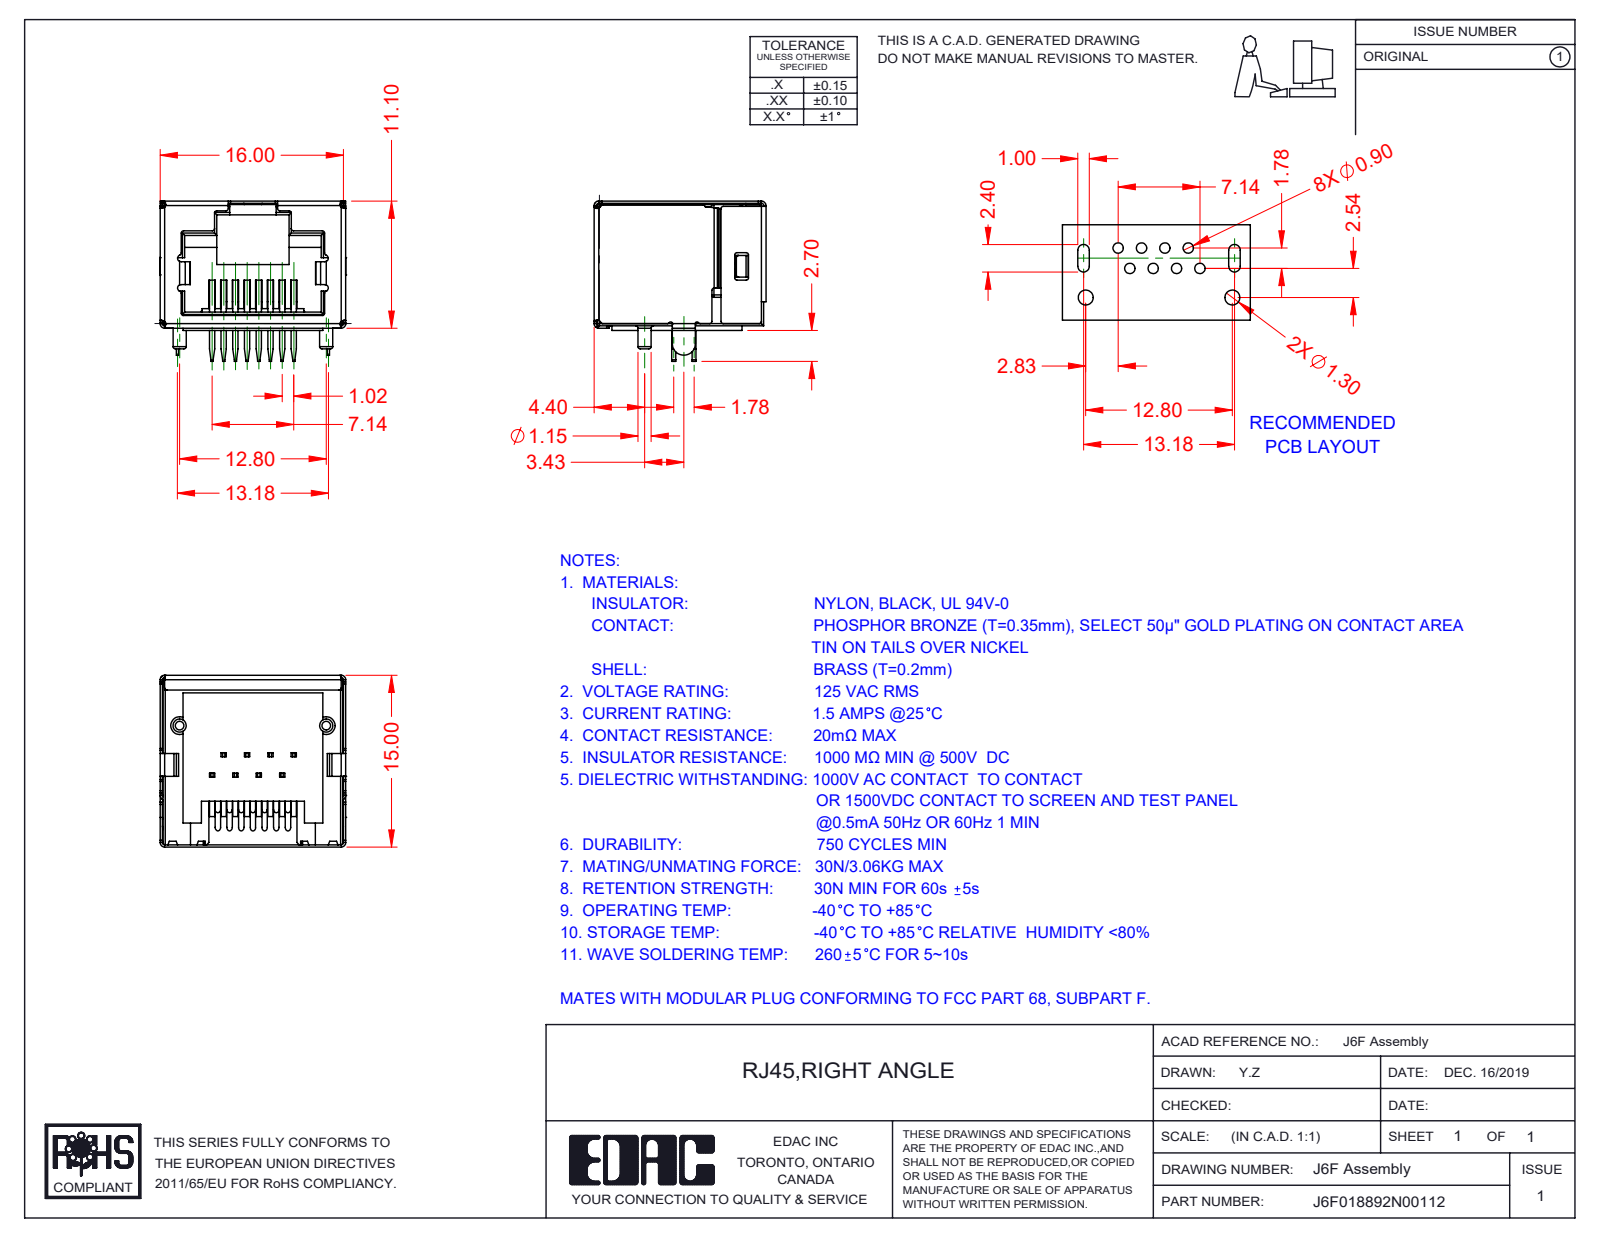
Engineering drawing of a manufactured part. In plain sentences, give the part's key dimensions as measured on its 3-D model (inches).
The part is named "6F Shield; J6F018892N00112; 6F Insulator; 6F Contacts". Its 3-D file was written by "SolidWorks 2016 (CONFIG_CONTROL_DESIGN)". It is 10 solids with 960 faces: 695 planar, 223 cylindrical and 42 other. Overall it measures 0.638 by 0.591 by 0.551 inches. Its volume is 0.082 cubic inches and its surface area 5.752 square inches. Round bosses or shafts: 2 of diameter 0.045. Partial cylindrical surfaces (rounded edges, fillets, slot ends): 77 of radius 0.008, 24 of radius 0.016, 20 of radius 0.012, 9 of radius 0.02, 7 of radius 0.009, 5 of radius 0.006, 4 of radius 0.004, 3 of radius 0.039. The main face-to-face distances are 0.62, 0.63, 0.628, 0.433, 0.618, 0.382, 0.437, 0.638, 0.622, 0.047.
